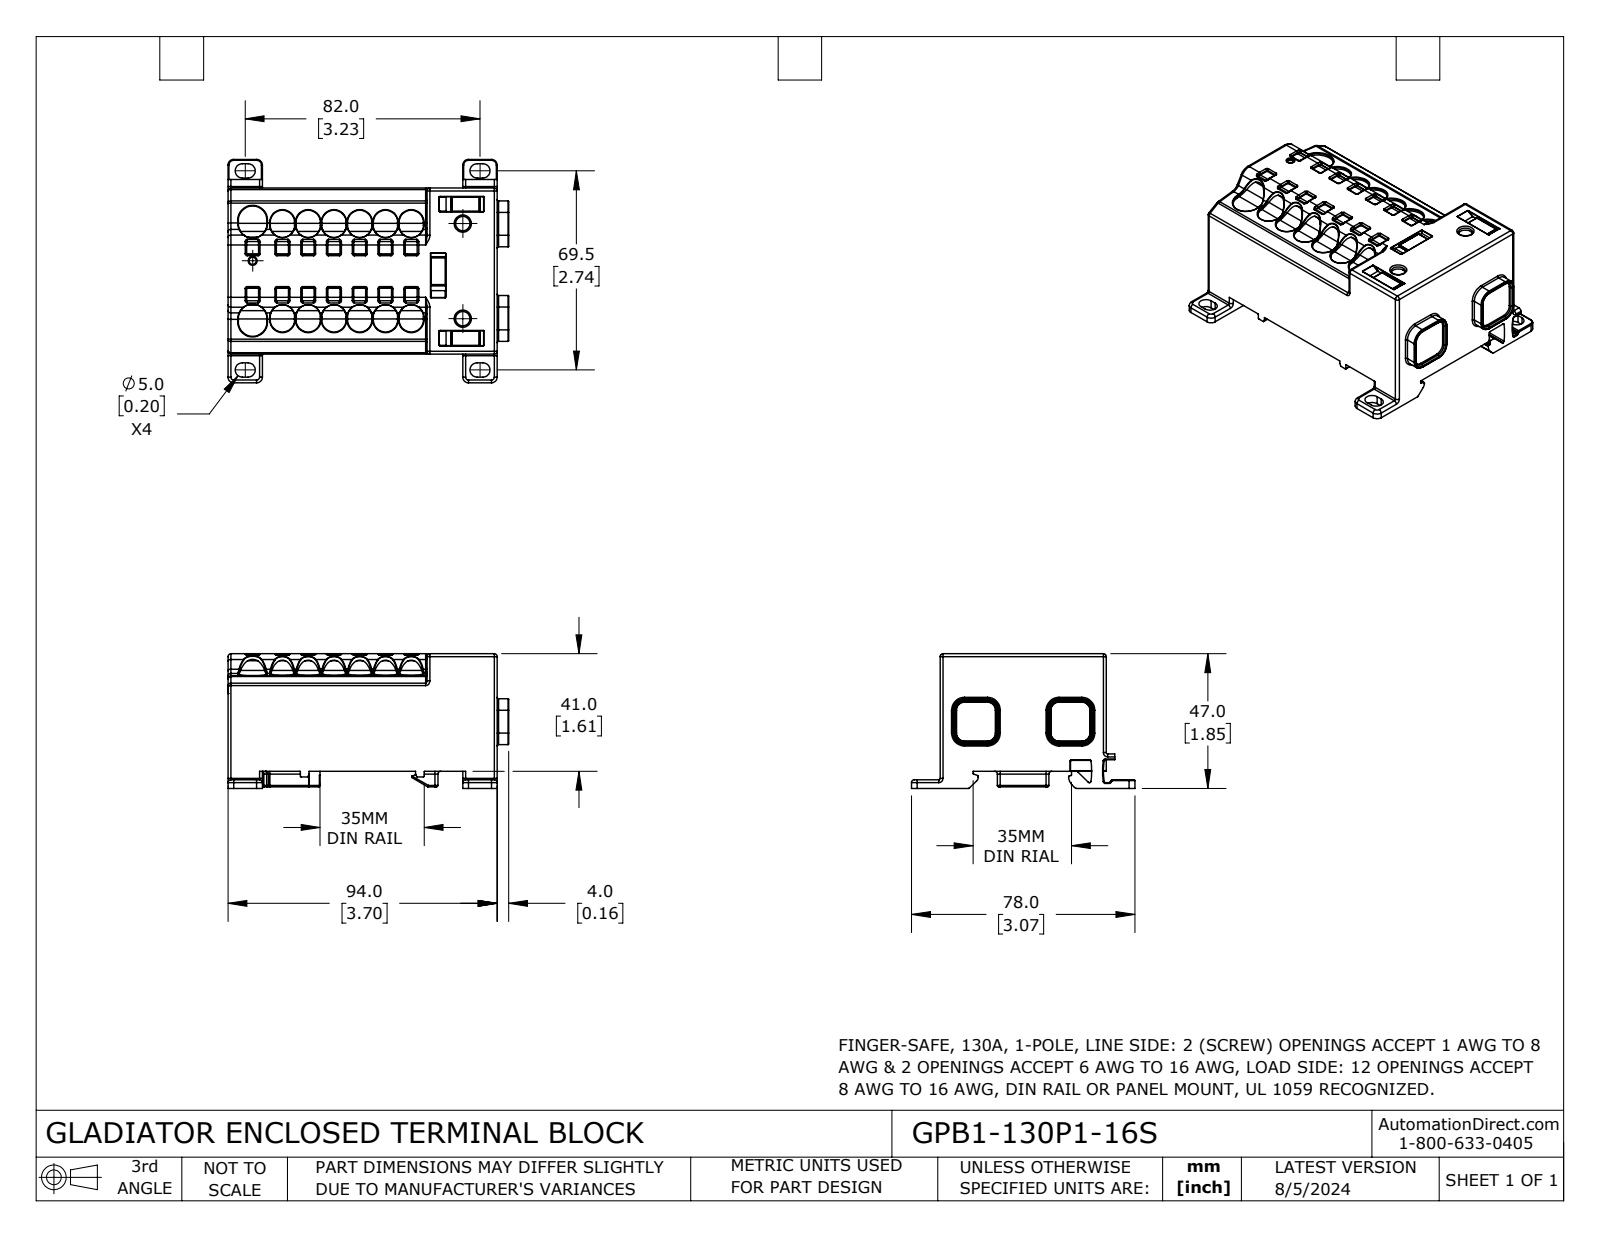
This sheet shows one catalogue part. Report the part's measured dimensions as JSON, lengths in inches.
{"part_name": "GPB1-130P1-16S", "step_written_by": "SolidWorks 2023 (CONFIG_CONTROL_DESIGN)", "units": "inches", "bodies": {"solids": 1, "faces": 1186, "planar": 308, "cylindrical": 509, "other": 369}, "overall_size": [3.858, 3.071, 1.85], "volume_in3": 12.97, "surface_area_in2": 42.28, "round_holes": [[0.197, 2], [0.098, 1]], "partial_cylinders_radius": [[0.008, 100], [0.02, 68], [0.004, 55], [0.039, 42], [0.167, 24], [0.012, 17], [0.079, 11], [0.157, 11]], "face_to_face_distances": [2.283, 1.614, 3.701, 0.236, 0.118, 1.85, 0.034, 0.02, 0.472, 1.831], "hole_center_spacings": [1.307, 2.935, 2.997]}
